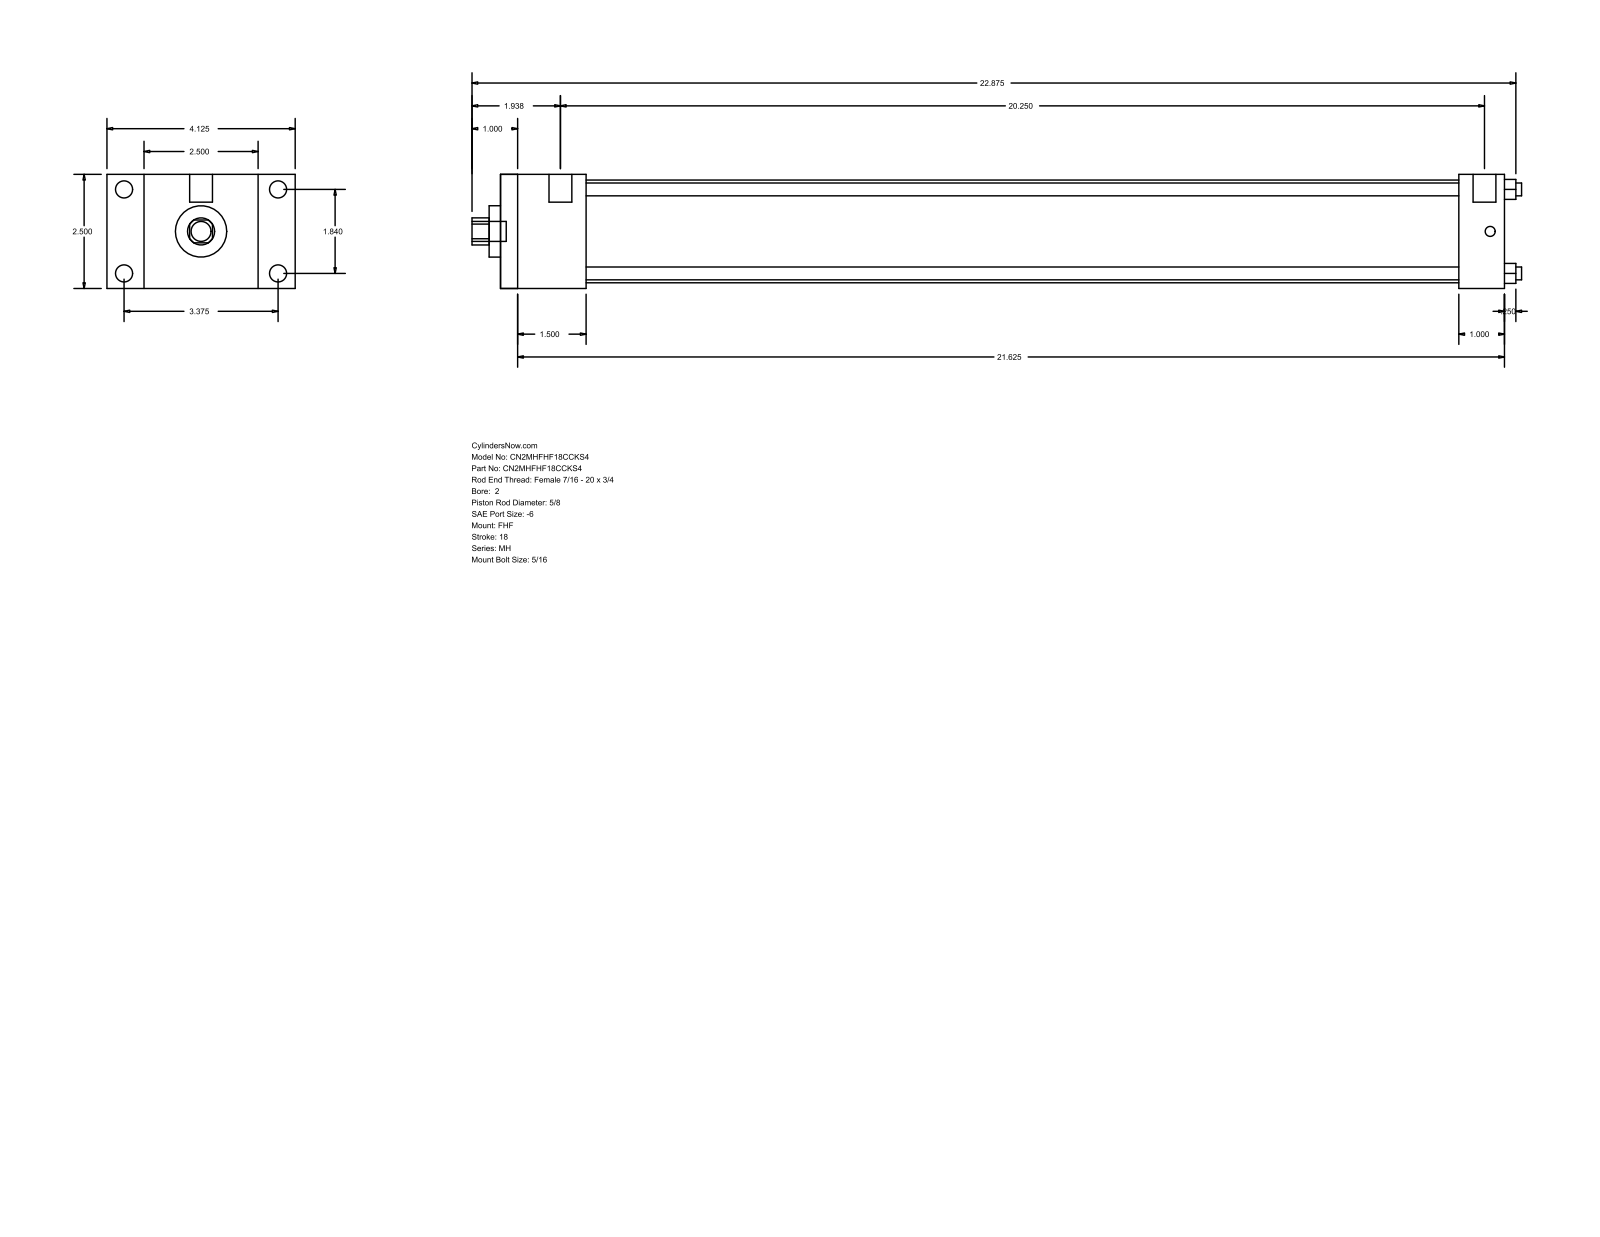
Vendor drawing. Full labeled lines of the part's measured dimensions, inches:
Part name (STEP PRODUCT): MH_FHF__0200_0.625
STEP written by: GSSL Pune (CONFIG_CONTROL_DESIGN)
Units: inches
Bodies: 0 solids, 88 faces (60 planar, 28 cylindrical, 0 other)
Overall size (bounding box): 23 × 4.125 × 2.5
Round holes (diameter × count): ⌀0.281 ×4, ⌀0.625 ×1, ⌀1.125 ×1, ⌀2.25 ×1
Round bosses / shafts (diameter × count): ⌀0.375 ×4, ⌀0.219 ×4, ⌀0.5 ×2, ⌀0.437 ×1
Partial cylindrical surfaces — rounded edges, fillets, slot ends (radius × count): R0.297 ×1
Main face-to-face distances: 2.5, 1.875, 22, 20.125, 0.813, 3.313, 4.125, 1, 21, 19.125
Hole centre spacings: 1.301, 1.84, 2.602
